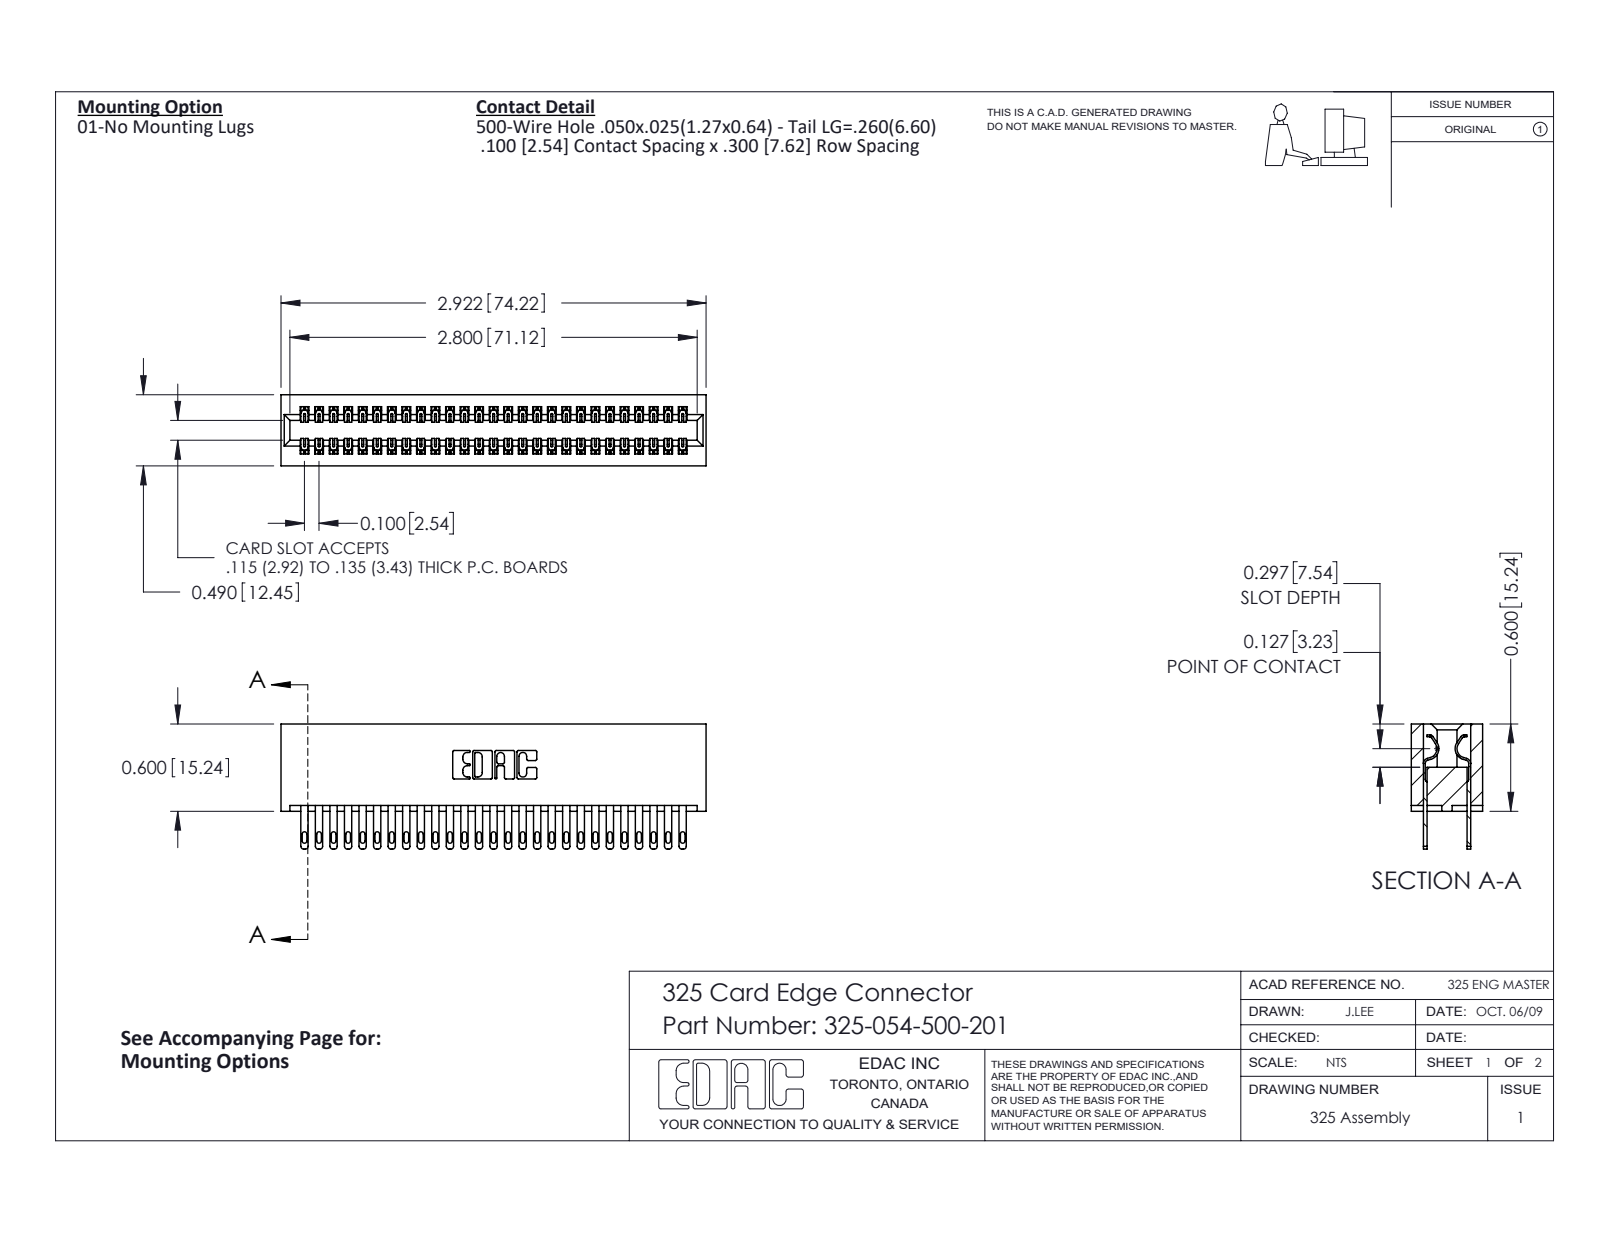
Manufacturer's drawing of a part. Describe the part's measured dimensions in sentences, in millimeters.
The part is named "325-292-001_325-293-100; 325 Part_Lugless; 325-054-500-201". Its 3-D file was written by "SolidWorks 2016 (CONFIG_CONTROL_DESIGN)". It is 55 solids with 2698 faces: 1686 planar, 1012 cylindrical and 0 other. Overall it measures 74.2 by 21.8 by 12.4 millimeters. Its volume is 10 200 cubic millimeters and its surface area 13 240 square millimeters. Partial cylindrical surfaces (rounded edges, fillets, slot ends): 81 of radius 0.2, 54 of radius 0.4, 54 of radius 0.5, 22 of radius 0.3, 6 of radius 0.2, 6 of radius 0.8, 3 of radius 0.7, 2 of radius 0.4. The main face-to-face distances are 2.1, 10.3, 7.6, 2.7, 9.7, 0.6, 8.3, 12.4, 7, 2.5.
